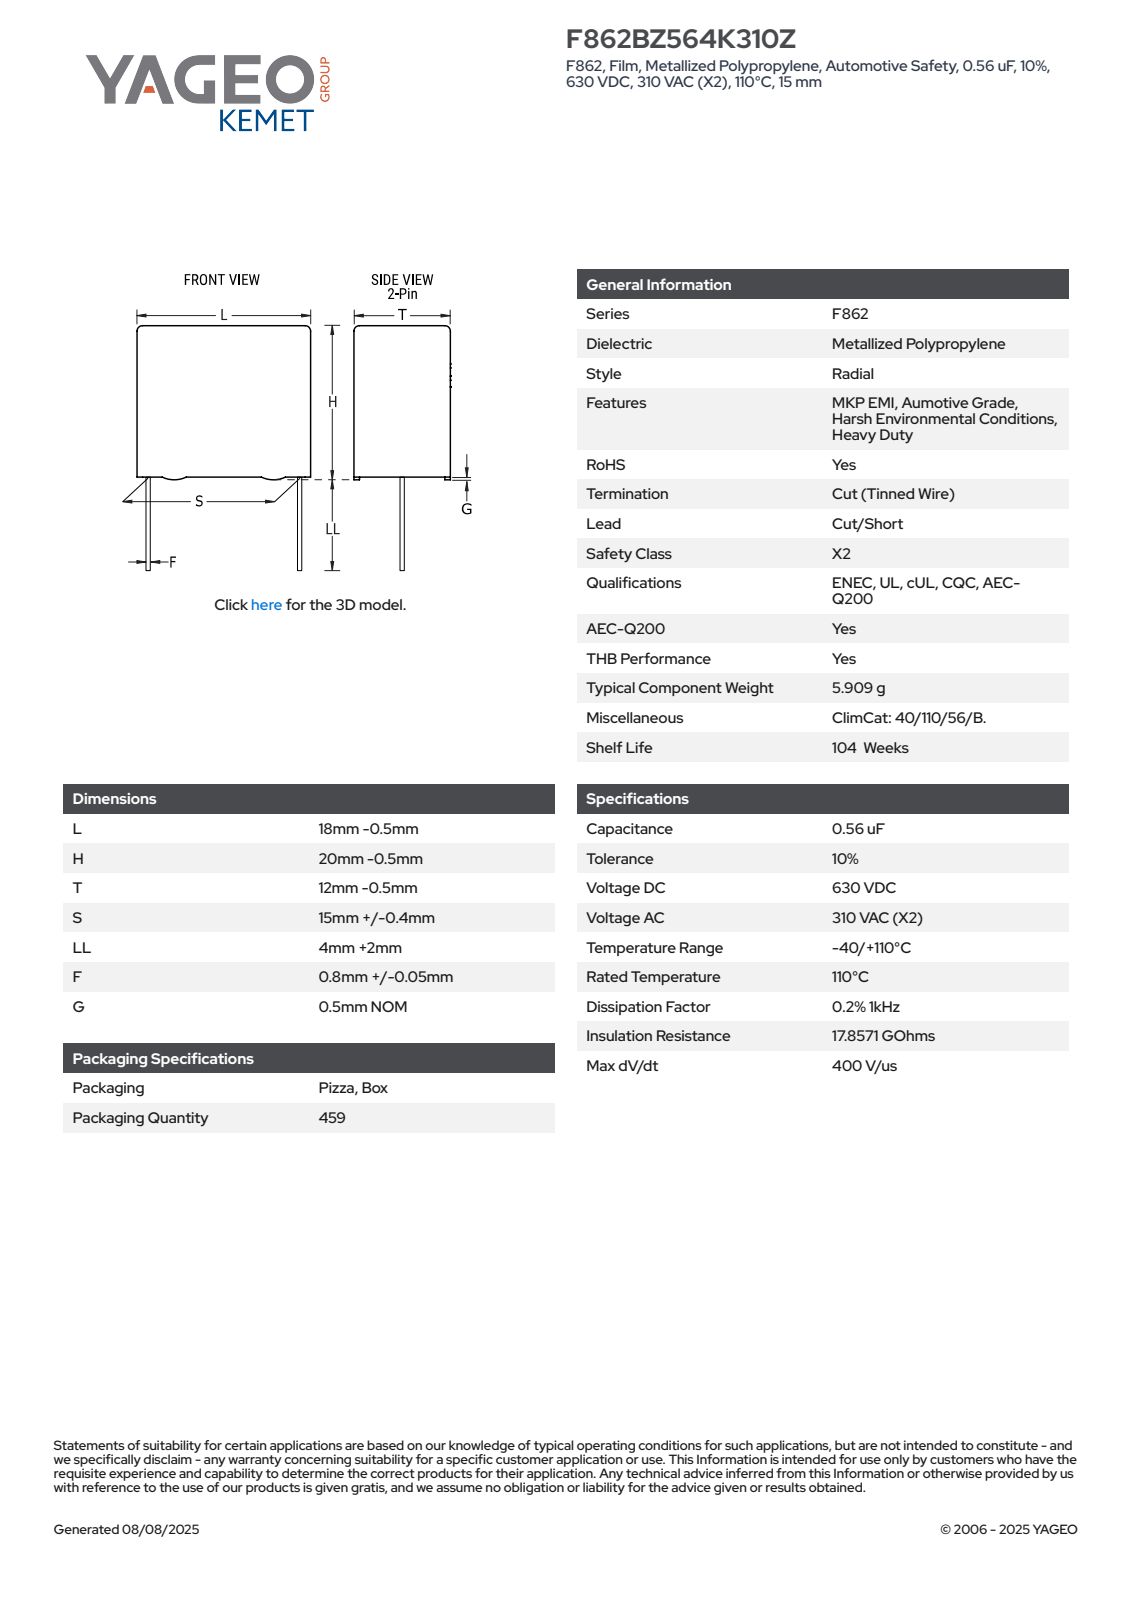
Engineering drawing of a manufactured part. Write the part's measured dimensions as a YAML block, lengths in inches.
part_name: "CFR_RBG_18X20X12_L17.5H19.5T11.5S15LL6F0.85G0.5"
step_written_by: "SolidWorks 2014 (AUTOMOTIVE_DESIGN)"
units: inches
bodies: {solids: 4, faces: 89, planar: 81, cylindrical: 8, other: 0}
overall_size: [1.004, 0.689, 0.453]
volume: 0.234
surface_area: 2.438
round_bosses_or_shafts:
  - {diameter: 0.033, count: 2}
partial_cylinders:
  - {radius: 0.02, count: 4}
face_to_face_distances: [0.453, 0.689, 0.748, 0.02, 0.768, 0.026, 0.427, 0.401, 0.236, 0.256]
